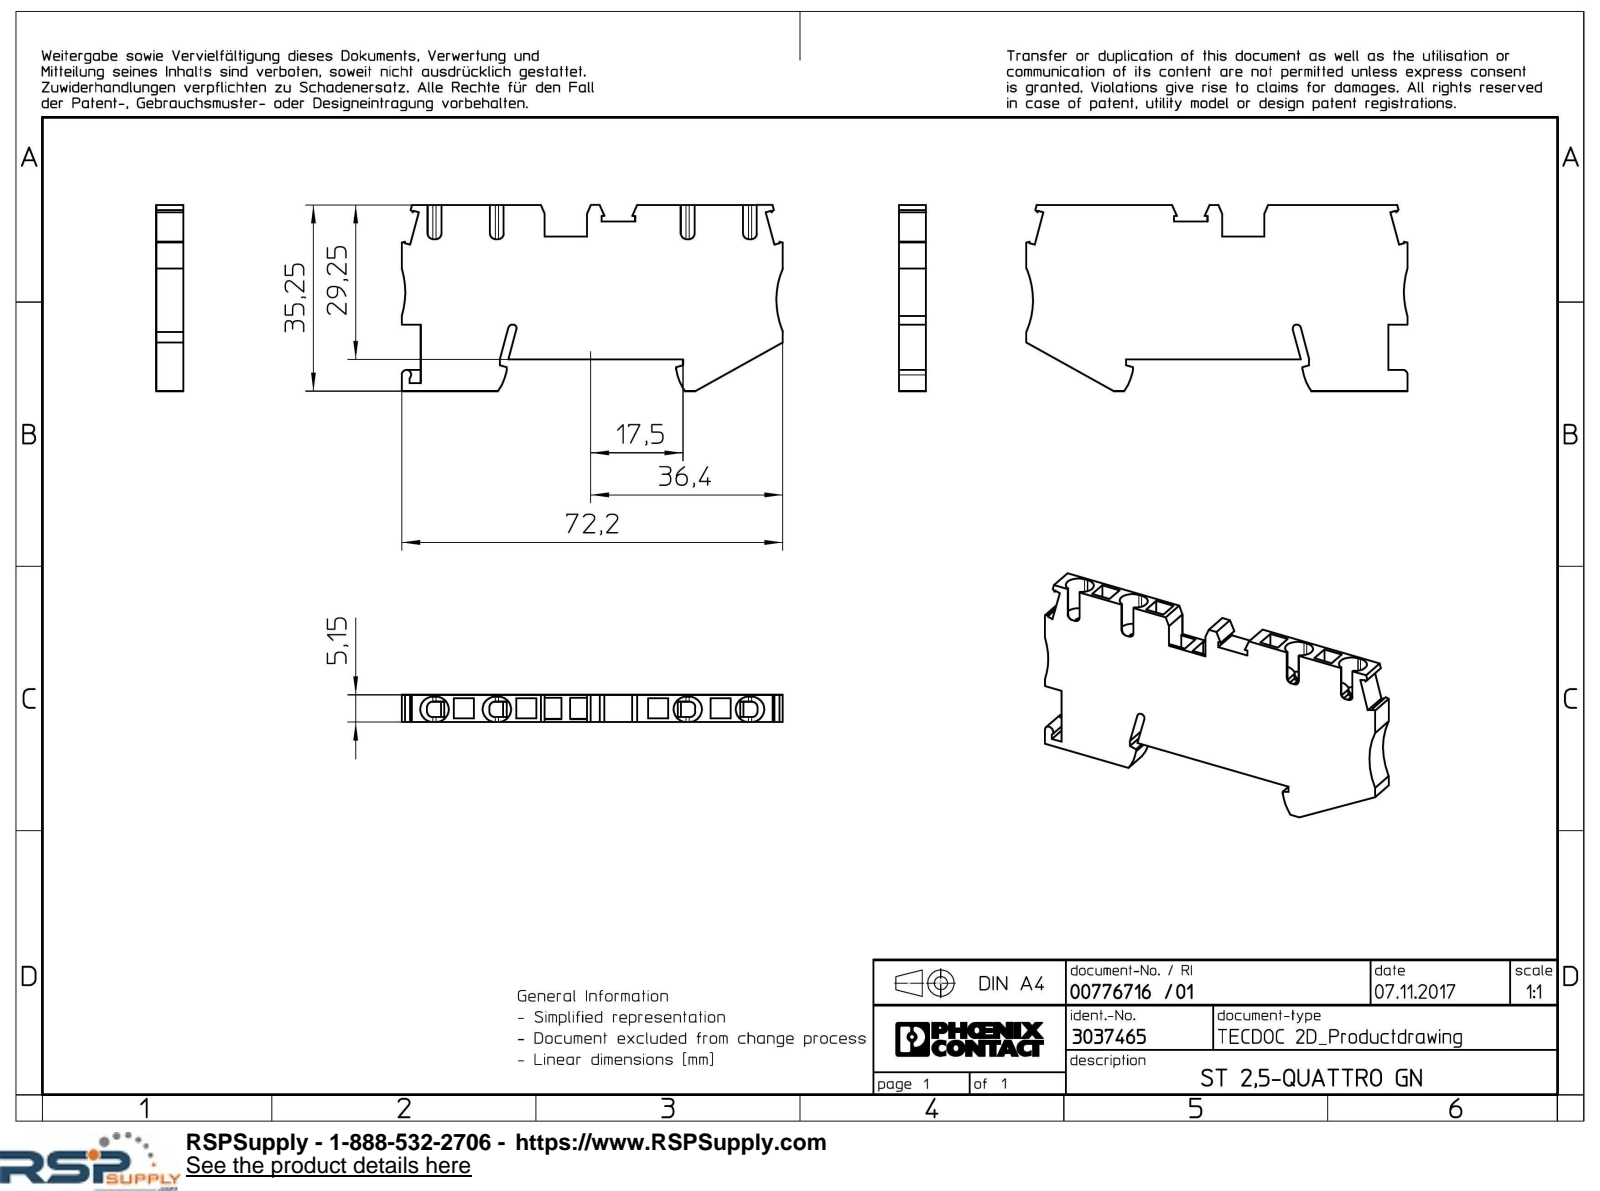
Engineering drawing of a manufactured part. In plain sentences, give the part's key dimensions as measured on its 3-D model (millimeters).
The part is named "ST_2.5-QUATTRO_GN-select". Its 3-D file was written by "Creo Elements/Direct Modeling 20.1A 29-Sep-2018 (C) Parametric Technology GmbH (AUTOMOTIVE_DESIGN)". It is 1 solid with 181 faces: 138 planar, 31 cylindrical and 12 other. Overall it measures 72.2 by 35.25 by 5.15 millimeters. Its volume is 9 313 cubic millimeters and its surface area 7 014 square millimeters. Partial cylindrical surfaces (rounded edges, fillets, slot ends): 16 of radius 1, 8 of radius 2.4, 2 of radius 9.5, 2 of radius 15, 1 of radius 0.7, 1 of radius 0.8, 1 of radius 0.9. The main face-to-face distances are 5.15, 3.8, 3.15, 0.65, 29.25, 11.8, 6, 4.45, 8, 35.25.
